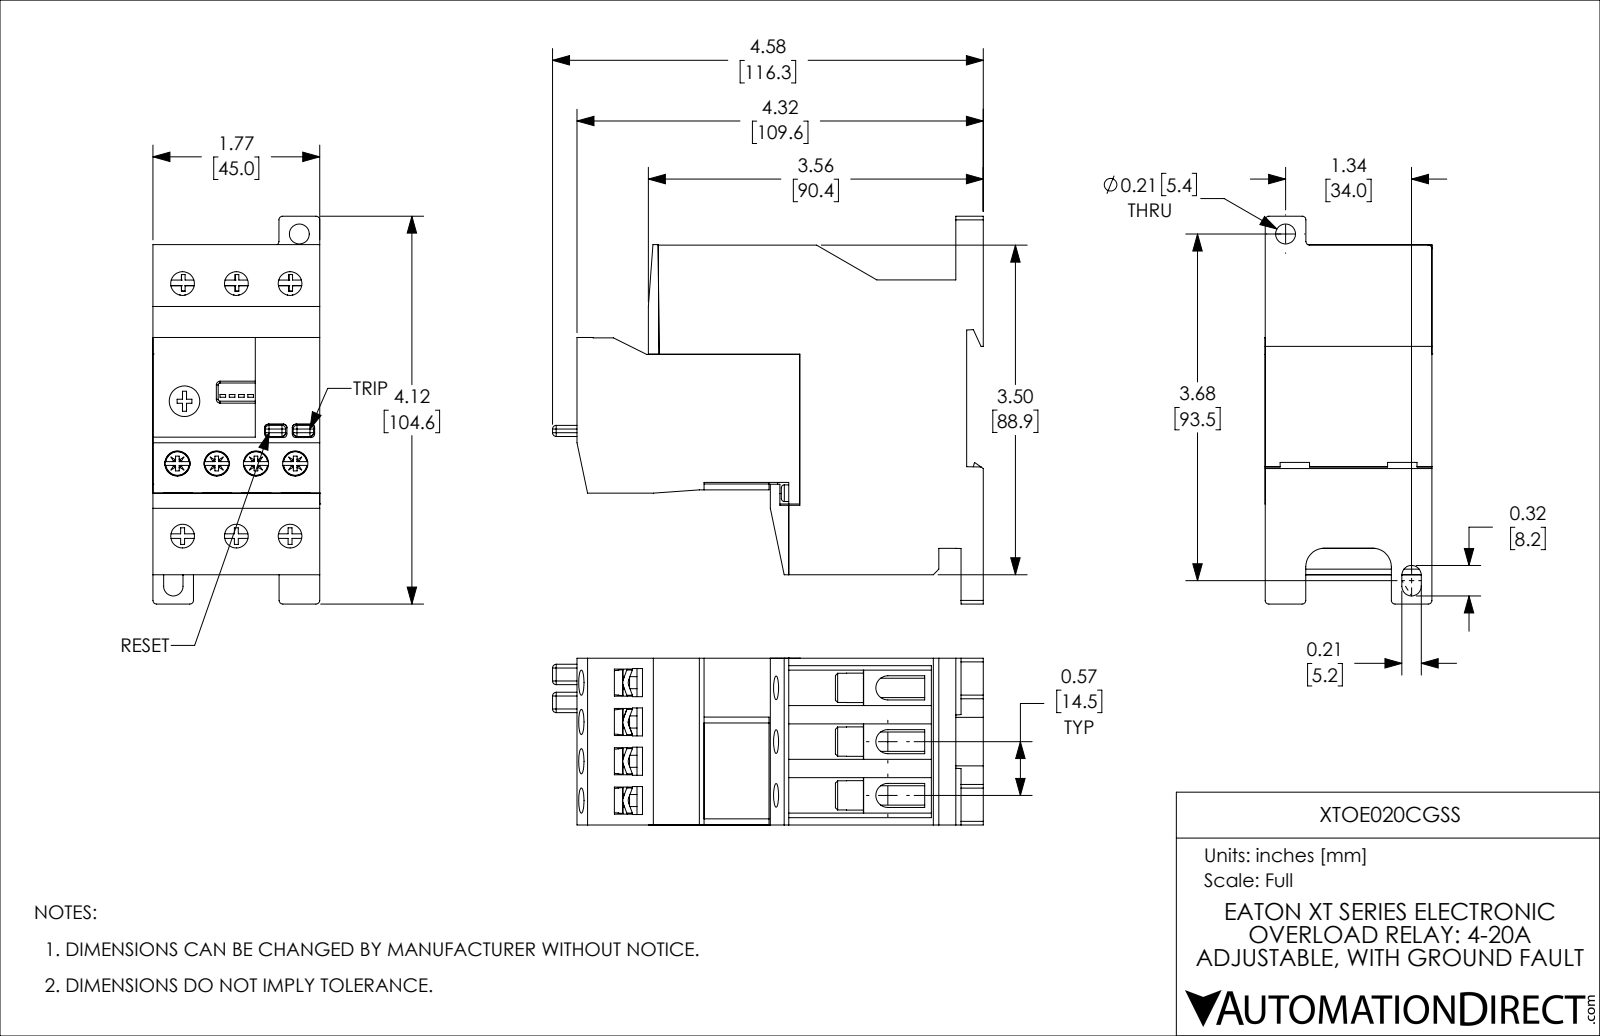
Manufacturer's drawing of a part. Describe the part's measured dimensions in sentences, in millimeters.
The part is named "XTOE020CGSS". Its 3-D file was written by "SolidWorks 2018 (AUTOMOTIVE_DESIGN)". It is 42 solids with 1296 faces: 854 planar, 281 cylindrical and 161 other. Overall it measures 116.25 by 104.6 by 45.01 millimeters. Its volume is 292 500 cubic millimeters and its surface area 75 869 square millimeters. Round holes: 6 of diameter 6.4, 5 of diameter 3.55, 4 of diameter 6.8, 3 of diameter 7.94, 2 of diameter 2.18, 2 of diameter 3.2, 1 of diameter 5.38. Round bosses or shafts: 4 of diameter 3.4, 4 of diameter 3.25, 4 of diameter 2.8, 4 of diameter 2.5, 3 of diameter 8, 2 of diameter 4.5, 1 of diameter 8.27. Partial cylindrical surfaces (rounded edges, fillets, slot ends): 64 of radius 0.5, 24 of radius 0.3, 22 of radius 1, 10 of radius 2, 6 of radius 3.25, 4 of radius 0.8, 3 of radius 0.4, 2 of radius 1.57. The main face-to-face distances are 45, 14.5, 1.87, 10.89, 4.5, 45.01, 44.99, 29, 49.5, 16.37. The hole center spacings are 10.6, 21.2, 10.59, 10.61, 19.63, 48.55, 48.82, 51.07.
